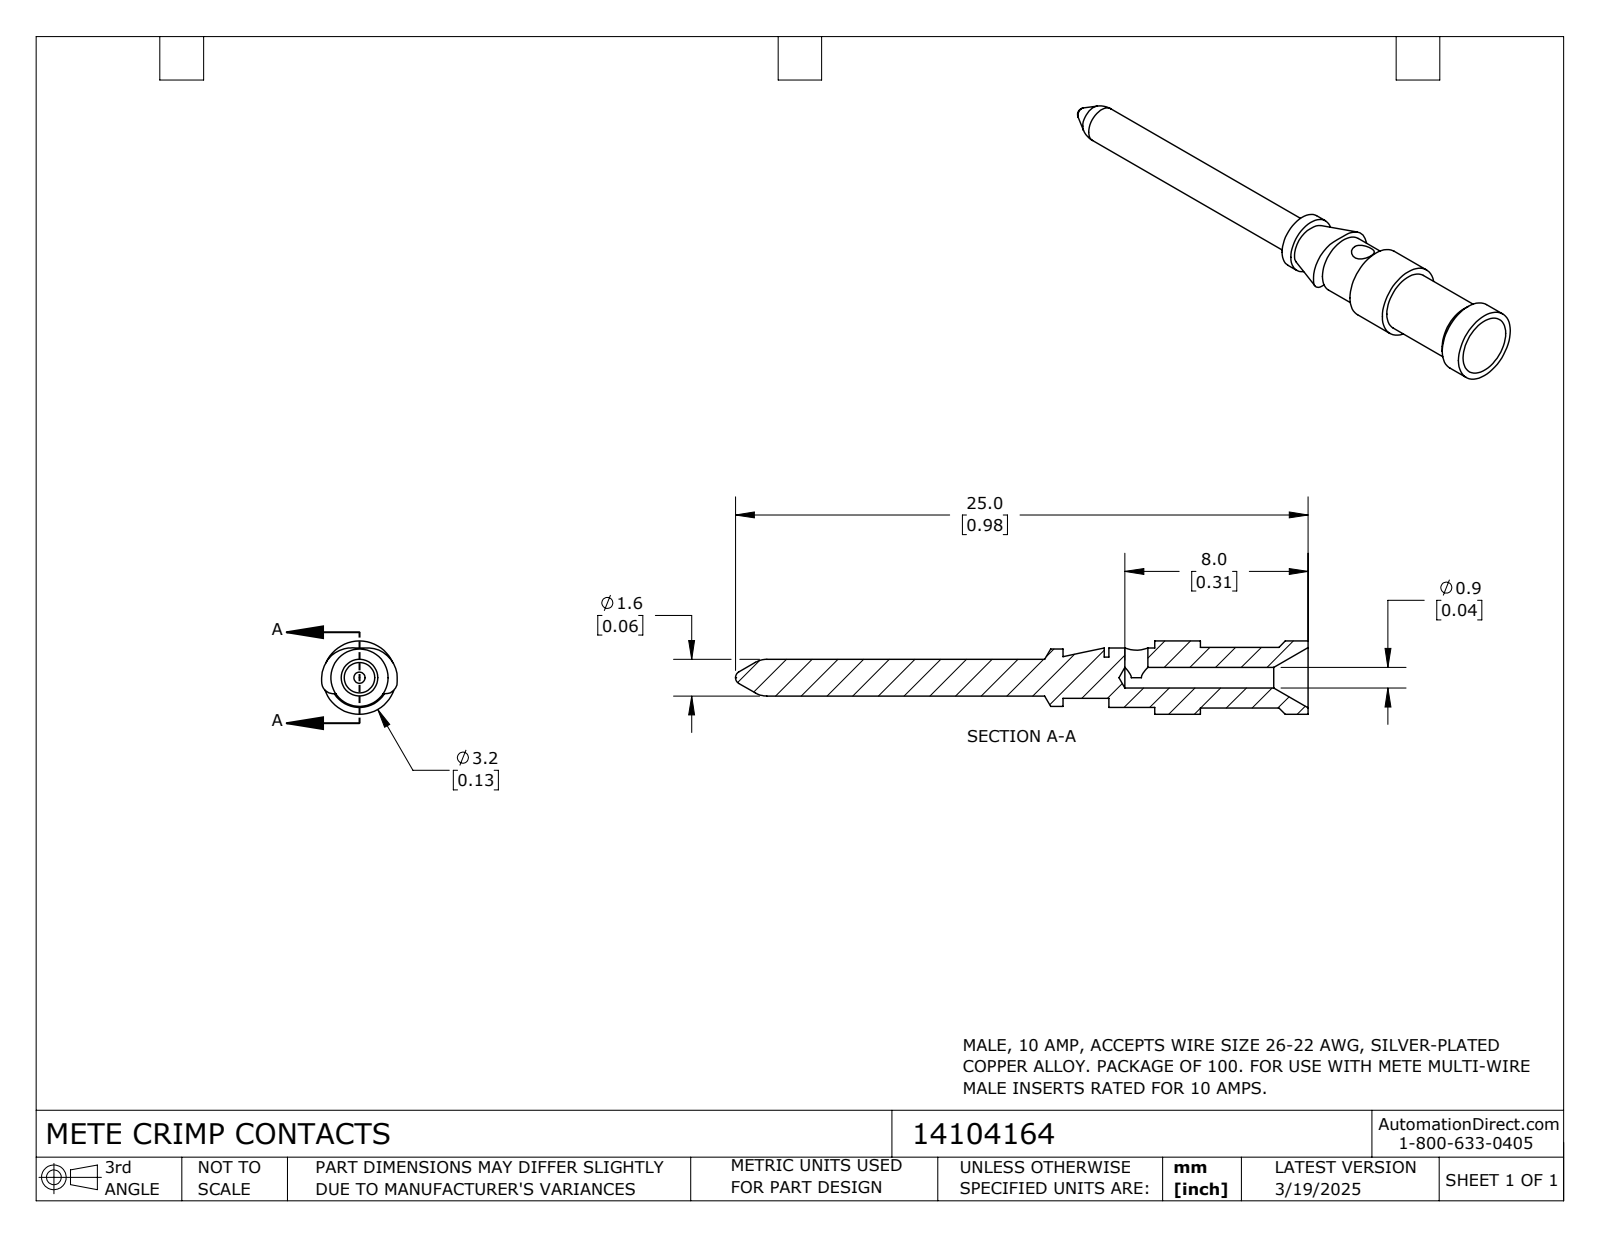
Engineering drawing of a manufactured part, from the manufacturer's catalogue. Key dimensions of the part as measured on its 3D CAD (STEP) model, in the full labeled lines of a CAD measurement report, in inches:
Part name (STEP PRODUCT): 14104164
STEP written by: SolidWorks 2024 (CONFIG_CONTROL_DESIGN)
Units: inches
Bodies: 1 solid, 44 faces (9 planar, 20 cylindrical, 15 other)
Overall size (bounding box): 0.984 × 0.13 × 0.126
Volume: 0.005 in³ · Surface area: 0.332 in²
Round holes (diameter × count): ⌀0.035 ×1, ⌀0.039 ×1
Round bosses / shafts (diameter × count): ⌀0.126 ×1, ⌀0.104 ×1, ⌀0.102 ×1, ⌀0.098 ×1, ⌀0.071 ×1, ⌀0.063 ×1
Main face-to-face distances: 0.079, 0.157, 0.087, 0.264, 0.343, 0.35, 0.185, 0.165, 0.421, 0.236
